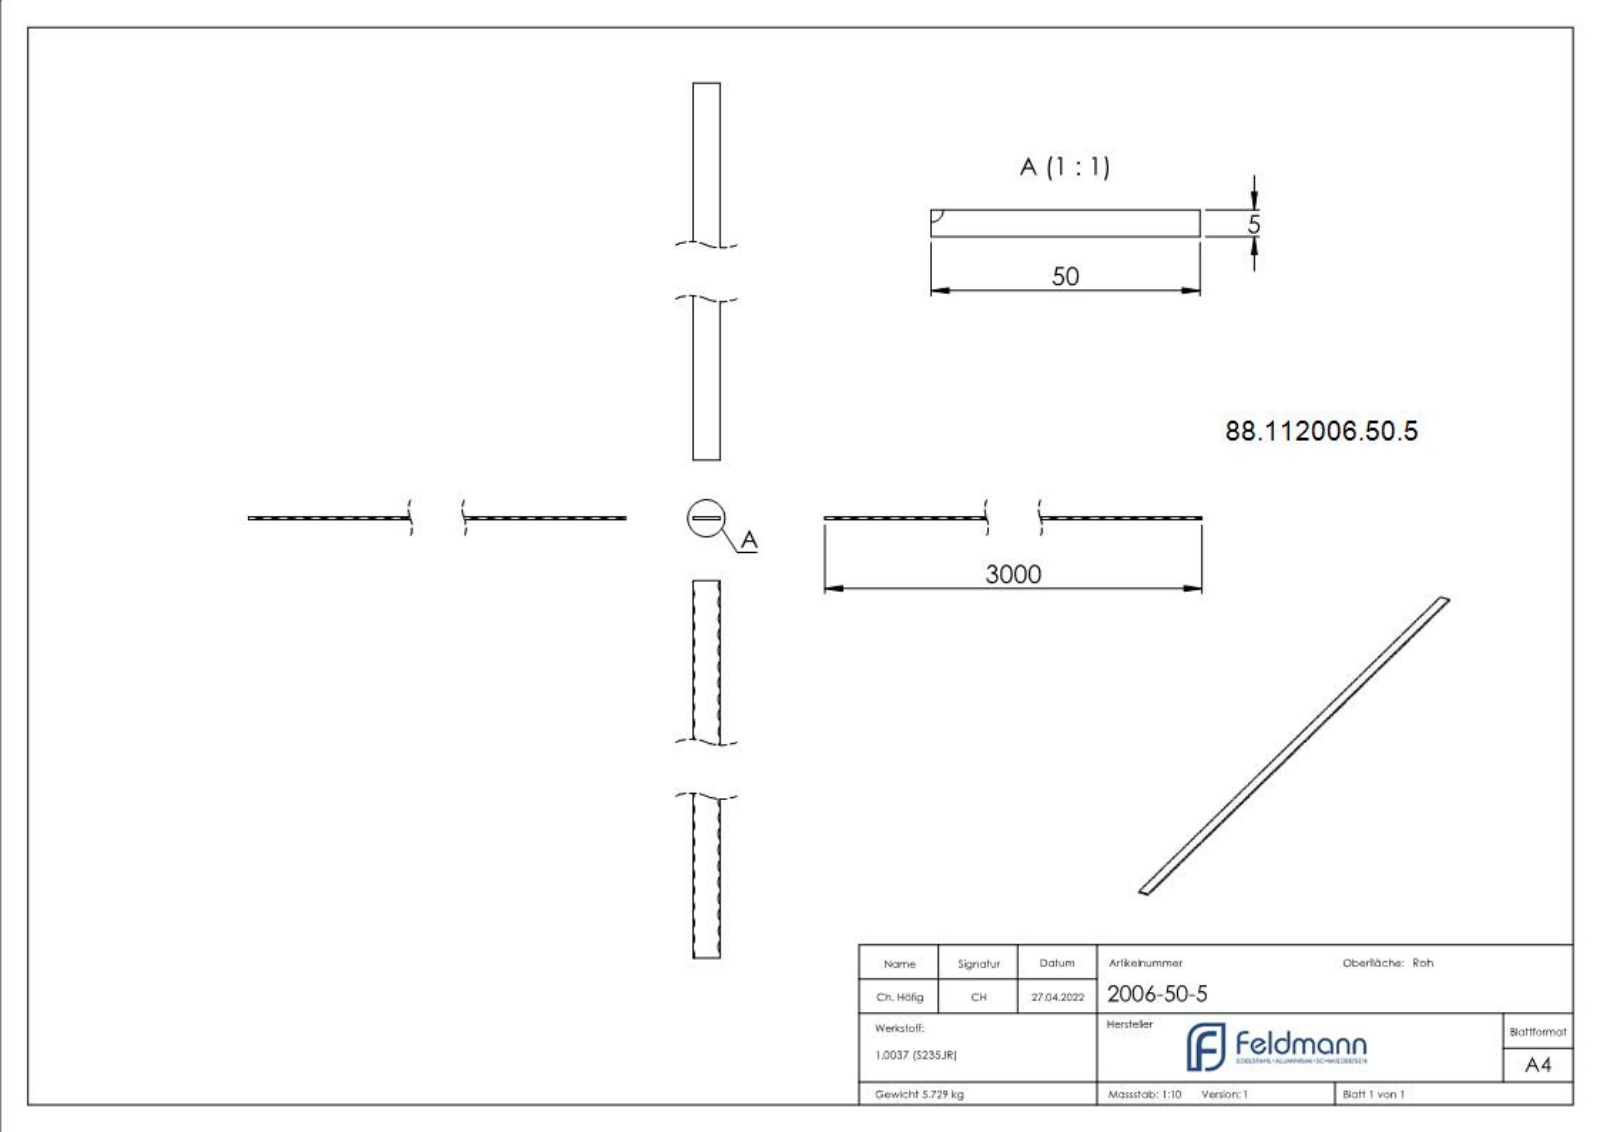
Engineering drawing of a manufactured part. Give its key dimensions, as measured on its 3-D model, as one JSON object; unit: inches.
{"part_name": "2006-50-5", "step_written_by": "SolidWorks 2018 (CONFIG_CONTROL_DESIGN)", "units": "inches", "bodies": {"solids": 1, "faces": 463, "planar": 136, "cylindrical": 0, "other": 327}, "overall_size": [118.11, 1.969, 0.197], "volume_in3": 44.82, "surface_area_in2": 507.5, "face_to_face_distances": [0.197, 1.969, 118.11, 0.193, 0.129, 0.013, 59.055, 0.944, 1.024, 0.054]}
